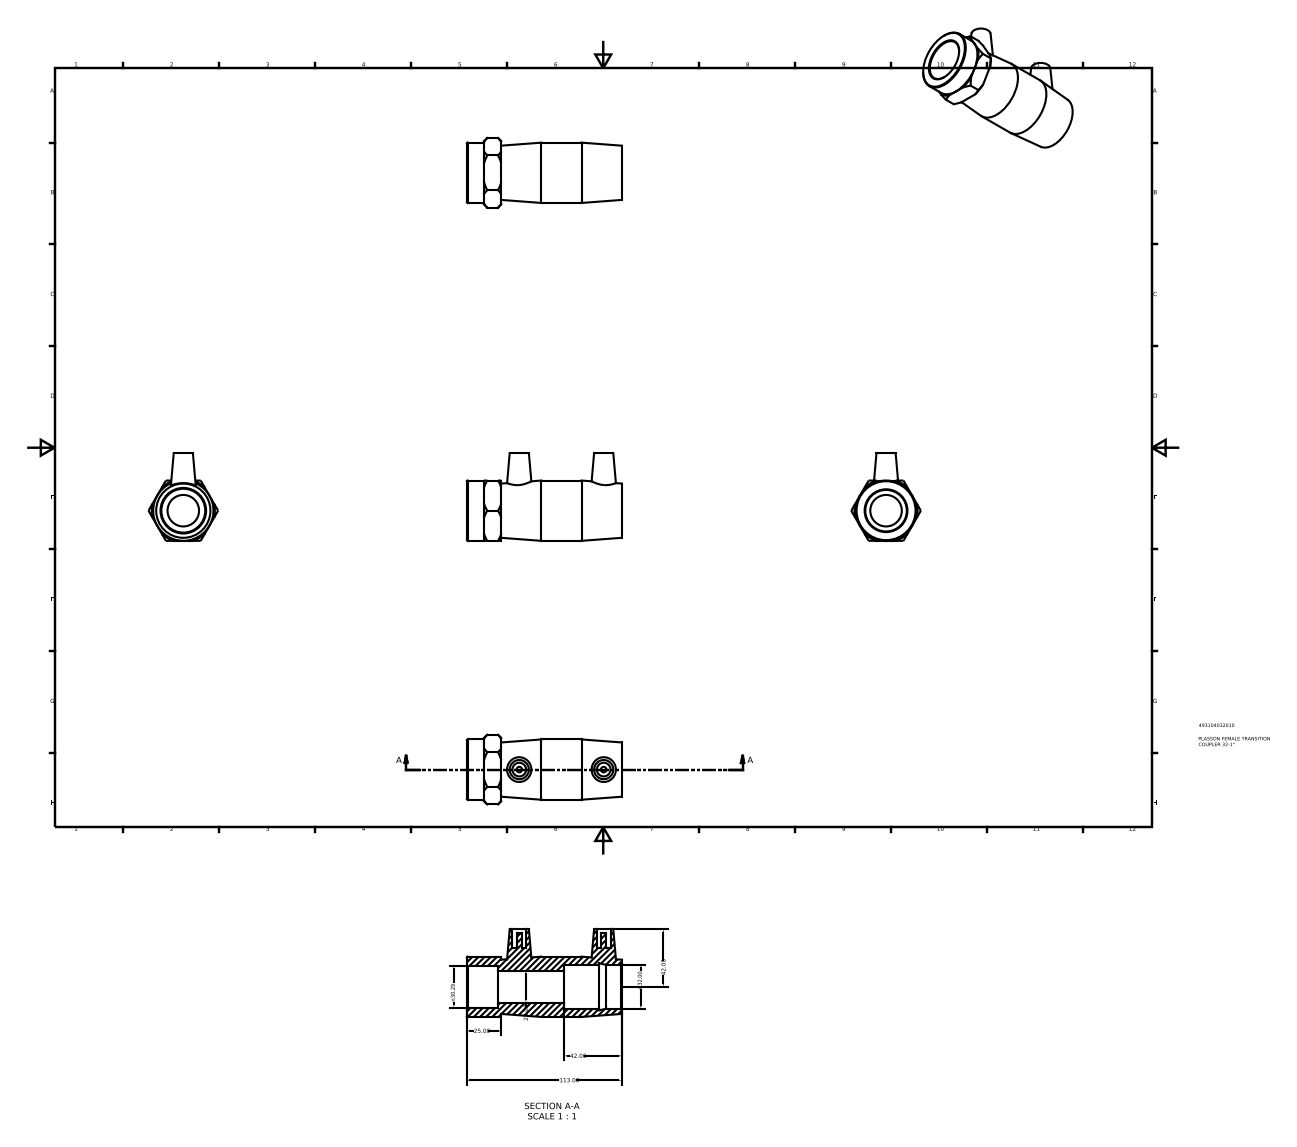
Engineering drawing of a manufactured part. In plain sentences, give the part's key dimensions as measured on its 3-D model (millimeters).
The part is named "493104032010". Its 3-D file was written by "Autodesk Inventor 2015 (AUTOMOTIVE_DESIGN)". It is 1 solid with 54 faces: 24 planar, 10 cylindrical and 20 other. Overall it measures 113 by 64 by 50.81 millimeters. Its volume is 101 260 cubic millimeters and its surface area 30 950 square millimeters. Round holes: 2 of diameter 10, 1 of diameter 23, 1 of diameter 30.29, 1 of diameter 32. Round bosses or shafts: 2 of diameter 4, 1 of diameter 44. The main face-to-face distances are 44, 71, 25, 46, 113, 88, 42, 22.5, 2.5, 48.5. The hole center spacings are 61.6.
